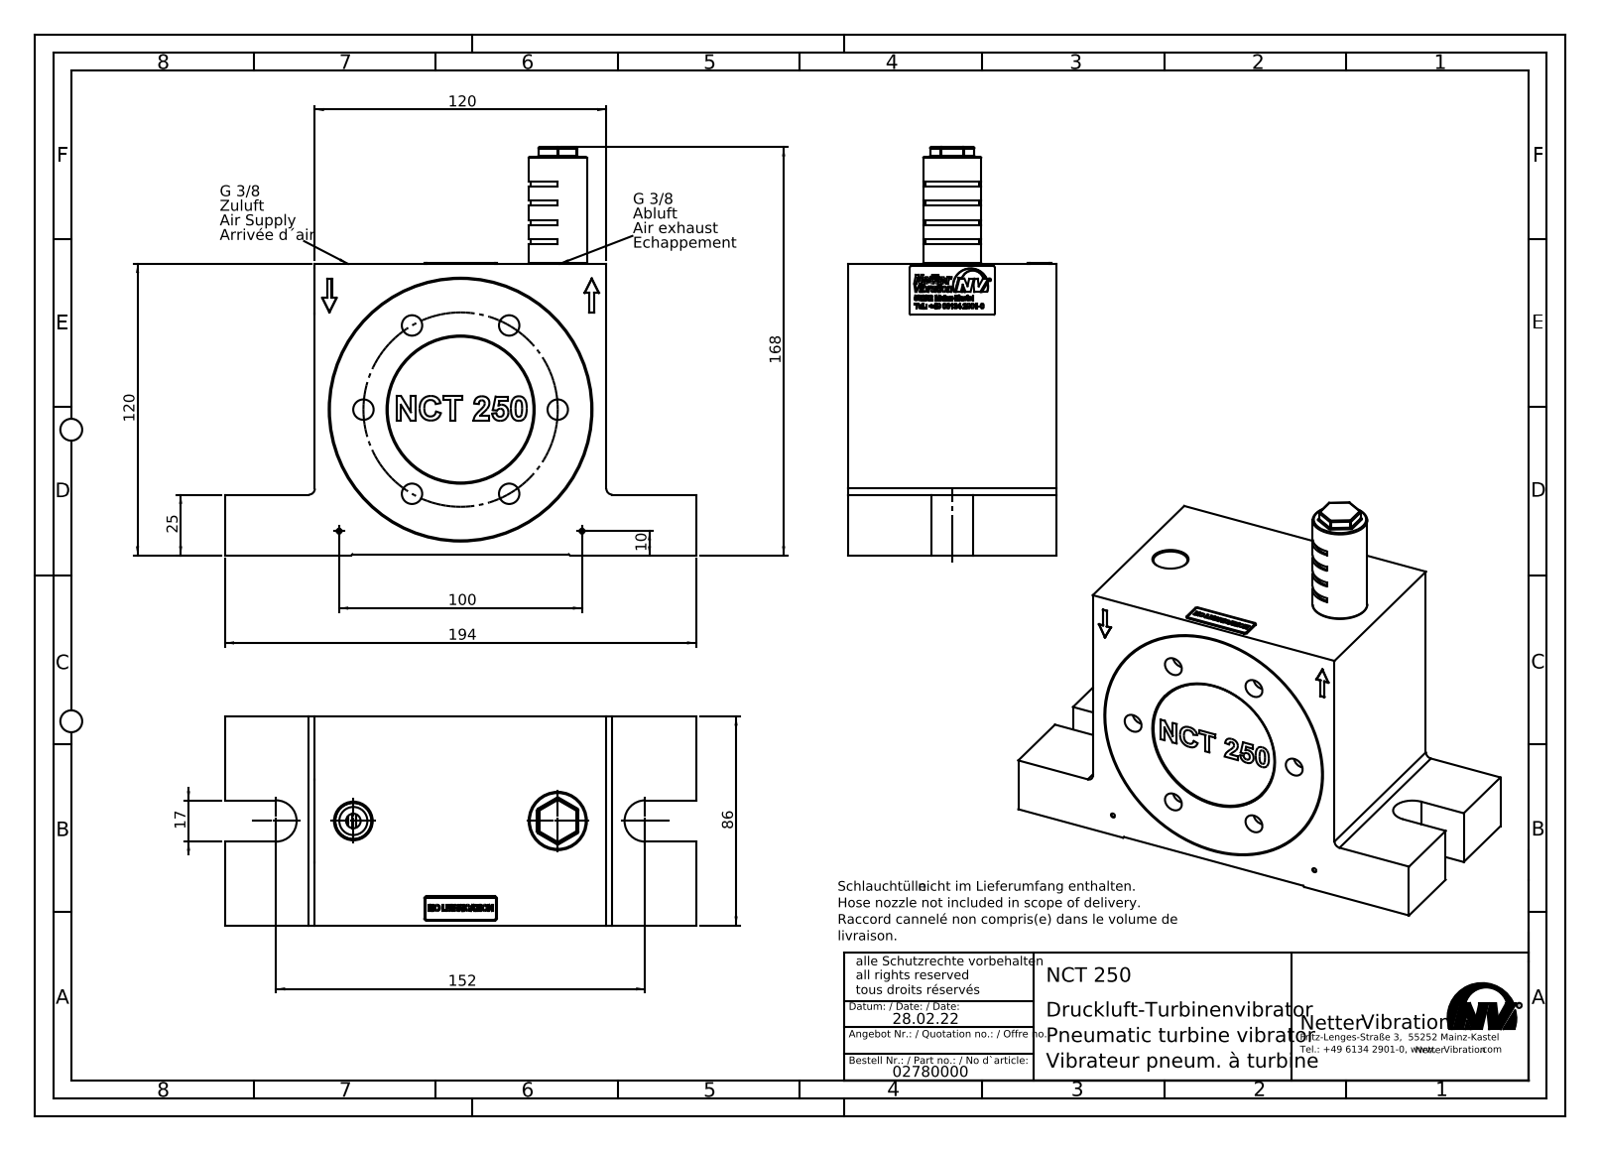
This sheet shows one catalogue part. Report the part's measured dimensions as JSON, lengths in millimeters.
{"part_name": "NCT 250 Turbinenvibrator #02780000", "step_written_by": "SolidWorks 2015 (AUTOMOTIVE_DESIGN)", "units": "millimeters", "bodies": {"solids": 6, "faces": 339, "planar": 209, "cylindrical": 77, "other": 53}, "overall_size": [194, 168, 86.25], "volume_mm3": 1487000, "surface_area_mm2": 132296, "round_holes": [[8.4, 6], [2, 2], [15, 2], [61, 1], [106.5, 1]], "round_bosses_or_shafts": [[109, 1], [106.47, 1], [103.87, 1], [60, 1], [24, 1], [16.66, 1]], "partial_cylinders_radius": [[0.5, 22], [1, 4], [2.5, 2], [8.5, 2], [11, 1]], "face_to_face_distances": [120, 0.5, 76, 65.25, 10.75, 119.5, 10, 86, 20.75, 24.5], "hole_center_spacings": [40, 69.28, 80, 32.45, 48.05, 68.62, 71.08, 86.98]}
